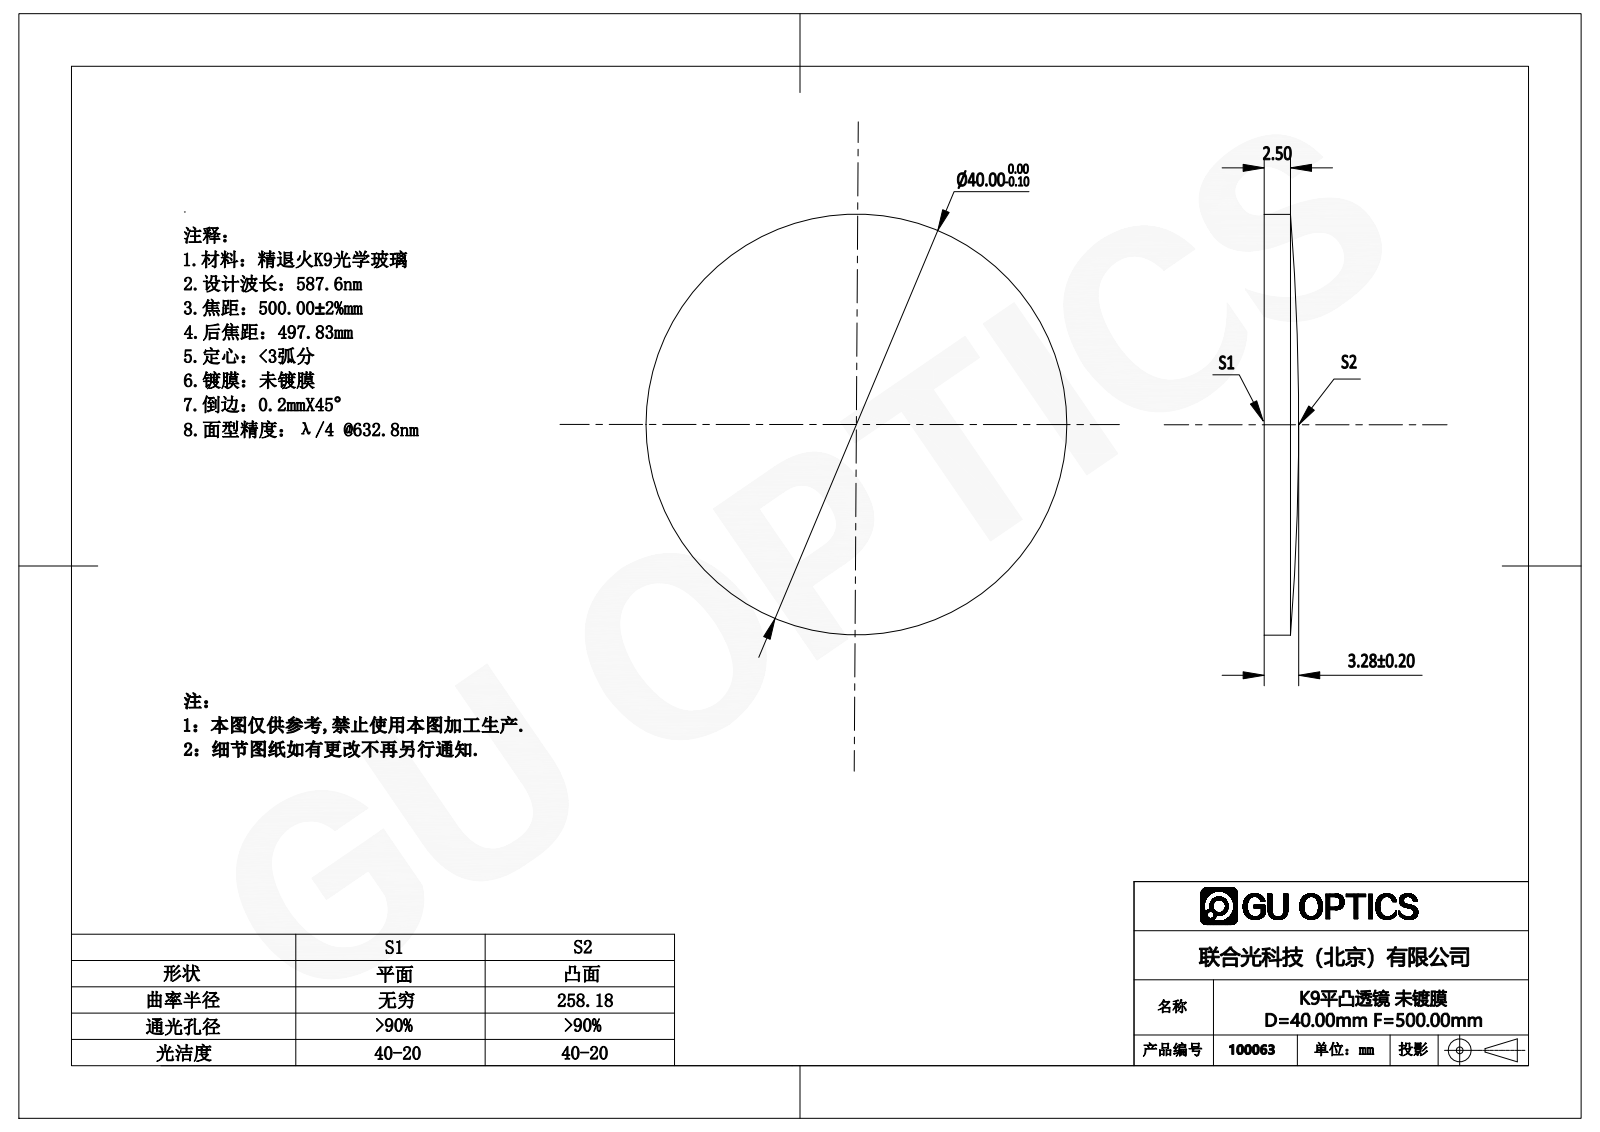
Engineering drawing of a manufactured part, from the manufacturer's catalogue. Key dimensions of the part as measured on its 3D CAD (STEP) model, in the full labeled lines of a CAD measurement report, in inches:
Part name (STEP PRODUCT): 100063
STEP written by: SolidWorks 2016 (AUTOMOTIVE_DESIGN)
Units: inches
Bodies: 1 solid, 5 faces (1 planar, 2 cylindrical, 2 other)
Overall size (bounding box): 1.575 × 1.575 × 0.129
Volume: 0.222 in³ · Surface area: 4.385 in²
Round bosses / shafts (diameter × count): ⌀1.575 ×1
